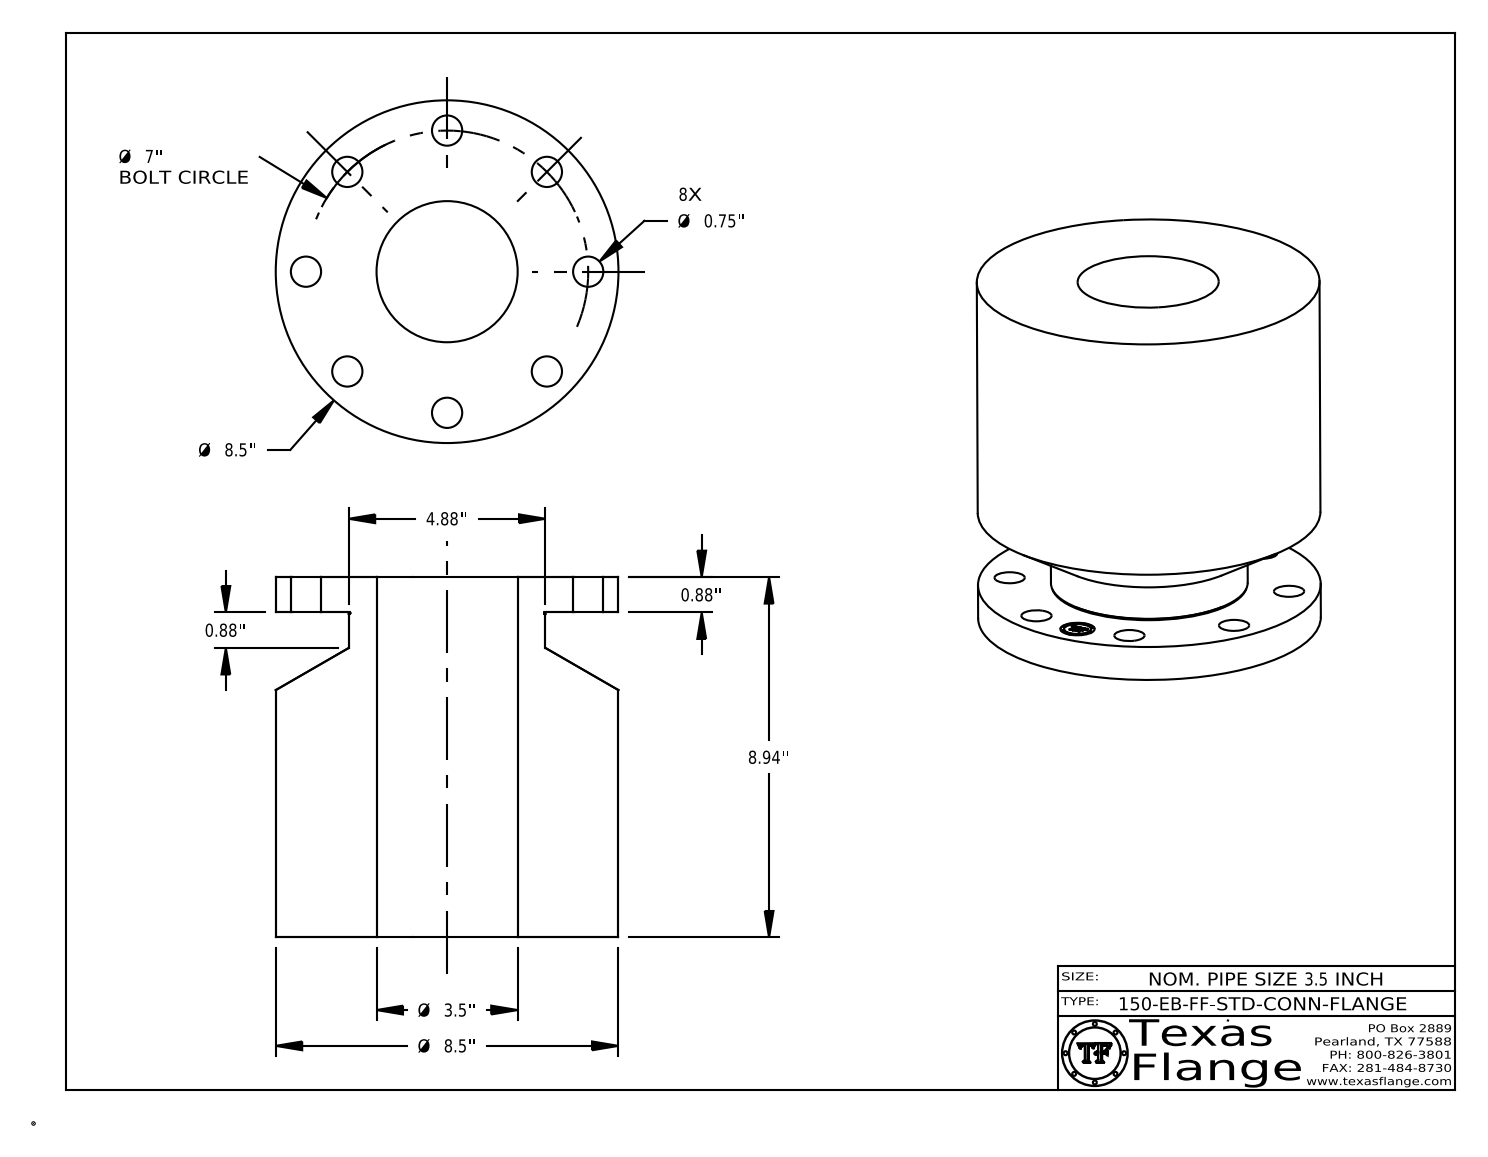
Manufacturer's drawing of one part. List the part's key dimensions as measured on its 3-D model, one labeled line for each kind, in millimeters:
Part name (STEP PRODUCT): 3.5-150-EB-FF-STD-CONN-FLANGE
STEP written by: CATIA V5 STEP AP214 (AUTOMOTIVE_DESIGN)
Units: millimetres
Bodies: 1 solid, 418 faces (368 planar, 44 cylindrical, 6 other)
Overall size (bounding box): 227 × 215.9 × 215.9
Volume: 5 947 000 mm³ · Surface area: 313 200 mm²
Round holes (diameter × count): ⌀19.1 ×8, ⌀21.6 ×1, ⌀88.9 ×1
Round bosses / shafts (diameter × count): ⌀1.3 ×8, ⌀215.9 ×1, ⌀124 ×1, ⌀17 ×1
Main face-to-face distances: 227, 22.3, 204.7, 22.1, 204.9, 6.5, 6.3, 0.4, 1.2, 4.2
Hole centre spacings: 88.9, 68, 125.7, 164.3, 34.7, 98.8, 147.8, 174.4
